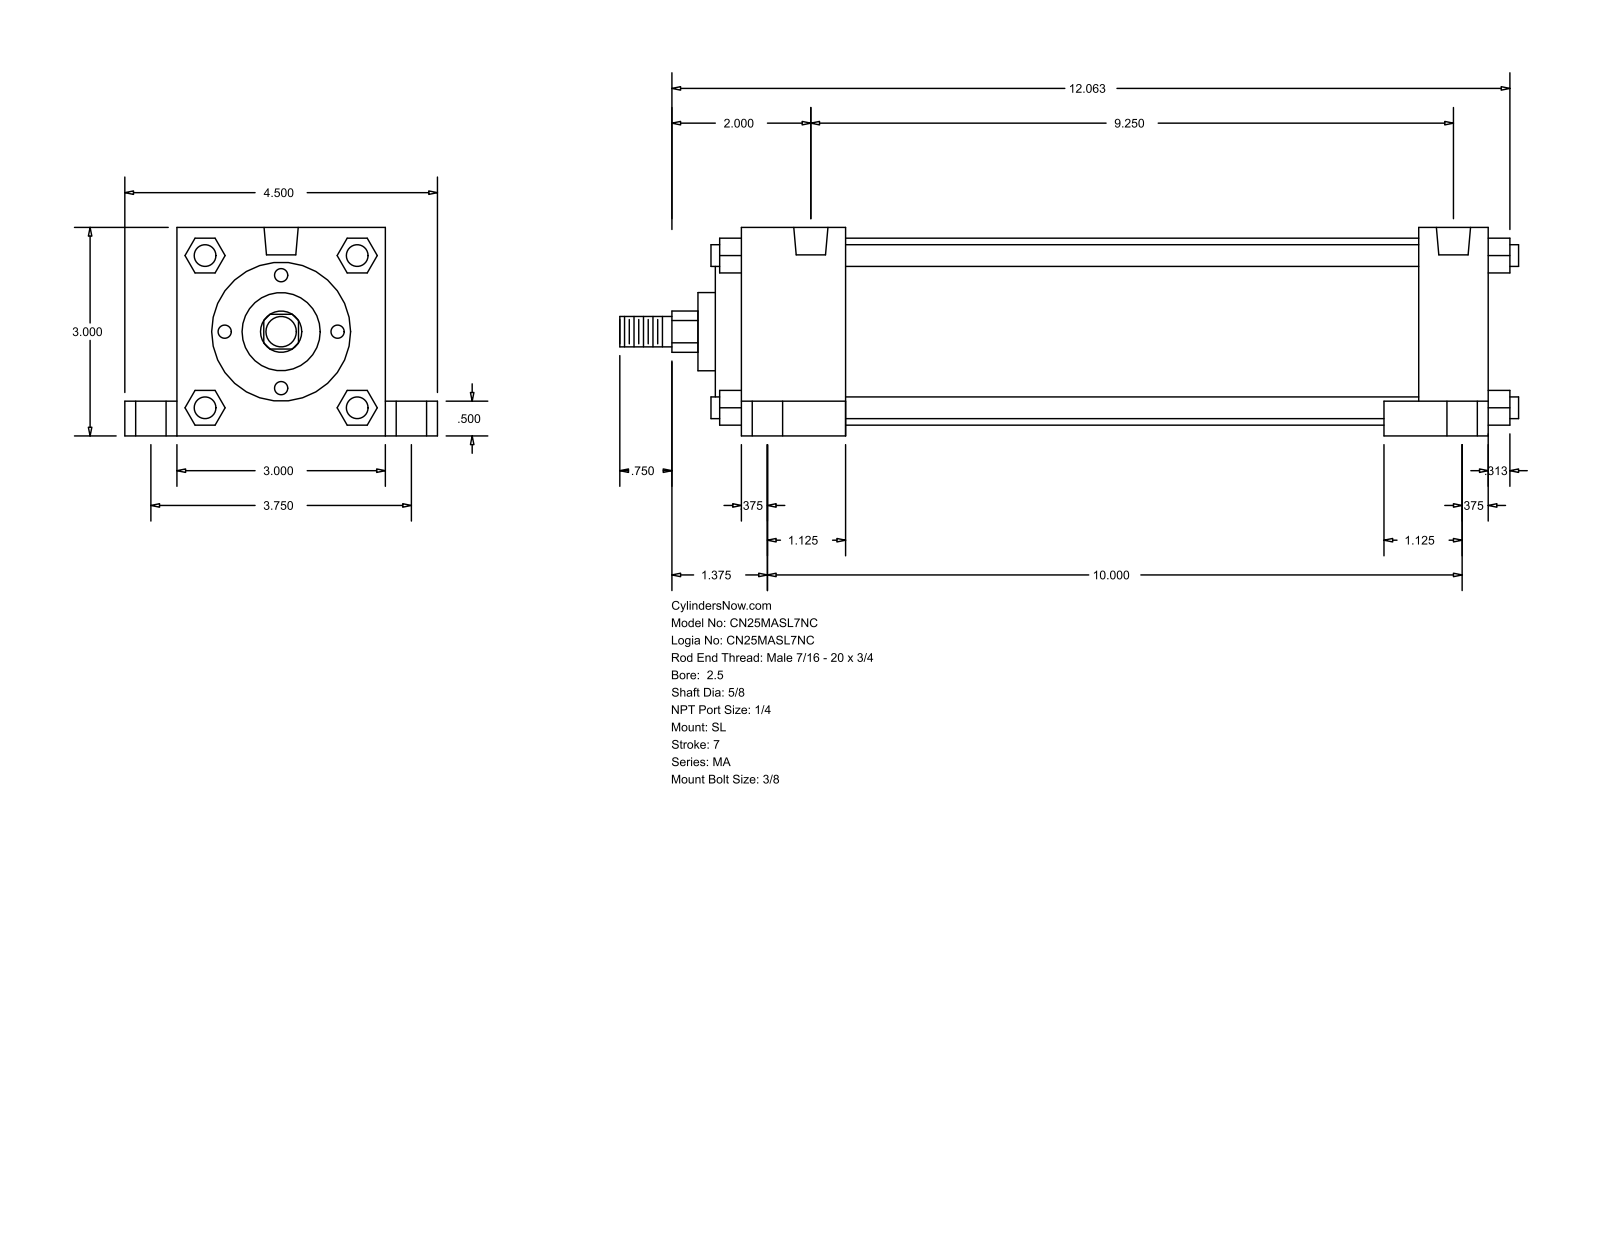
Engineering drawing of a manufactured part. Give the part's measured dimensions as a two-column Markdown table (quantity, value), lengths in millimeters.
| quantity | value |
| --- | --- |
| part name | MA_SL__0250_0.625 |
| STEP written by | GSSL Pune (CONFIG_CONTROL_DESIGN) |
| units | millimeters |
| bodies | 0 solids, 150 faces (113 planar, 37 cylindrical, 0 other) |
| overall size | 328.61 × 114.3 × 76.2 |
| round holes (diameter × count) | 7.94 × 4, 11.11 × 4, 17.46 × 4, 12.49 × 2 |
| round bosses / shafts (diameter × count) | 7.94 × 4, 68.33 × 1, 50.8 × 1, 28.57 × 1, 15.88 × 1, 11.11 × 1 |
| partial cylindrical surfaces (radius × count) | 7.54 × 1 |
| main face-to-face distances | 76.2, 273.05, 12.7, 209.55, 25.4, 38.1, 234.95, 247.65, 19.05, 63.5 |
| hole center spacings | 47.73, 50.2, 95.24, 234.95, 242.84, 254.01, 255.31, 271.28 |
